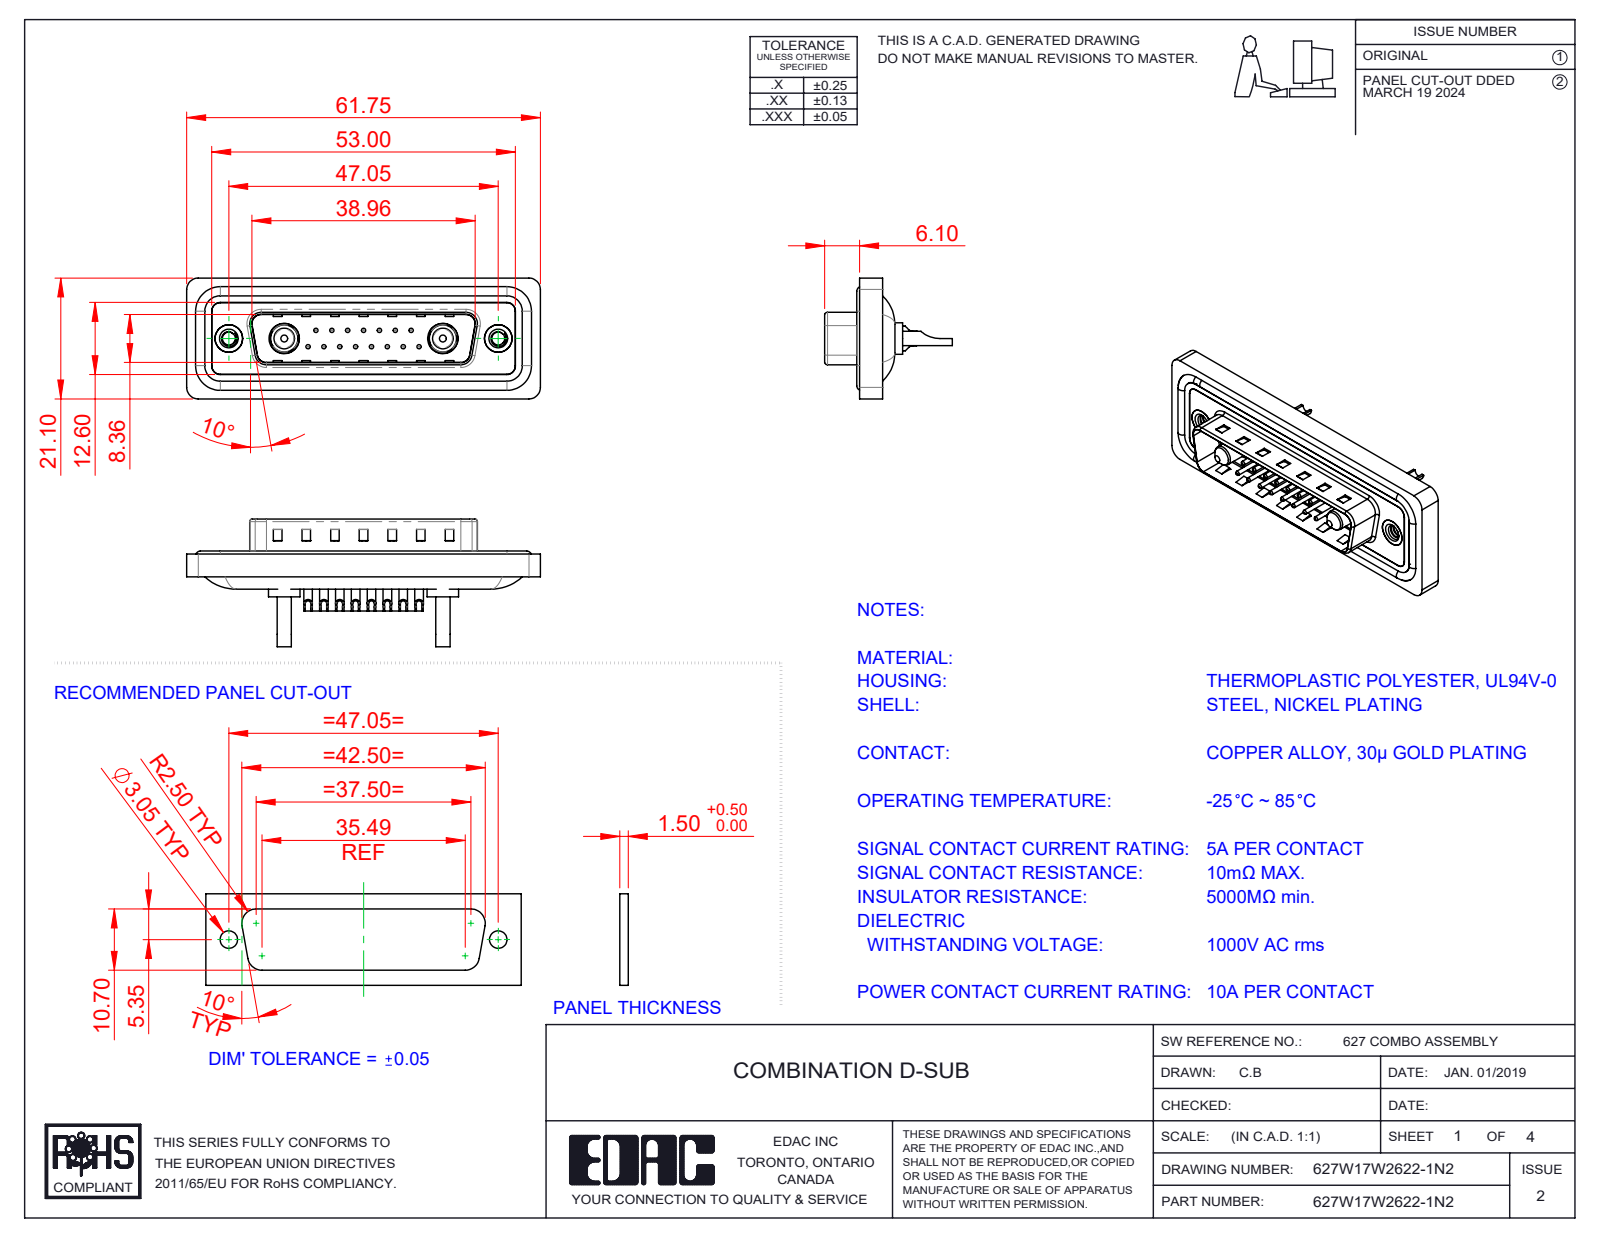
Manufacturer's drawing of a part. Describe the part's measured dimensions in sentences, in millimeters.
The part is named "627Combo Contact Row 1_22; 627Combo Threaded Rivet_2; 627Combo Housing_17W2; 627Combo Contact Row 2_22 (+5 more)". Its 3-D file was written by "SolidWorks 2023 (CONFIG_CONTROL_DESIGN)". It is 26 solids with 1128 faces: 368 planar, 472 cylindrical and 288 other. Overall it measures 61.75 by 22.3 by 21.1 millimeters. Its volume is 7 284 cubic millimeters and its surface area 12 129 square millimeters. Round holes: 15 of diameter 0.75, 15 of diameter 1, 15 of diameter 1.6, 15 of diameter 2, 2 of diameter 1.7, 2 of diameter 2.26, 2 of diameter 4, 2 of diameter 4.8, 2 of diameter 4.85, 2 of diameter 5, 2 of diameter 5.3. Round bosses or shafts: 15 of diameter 1.5, 4 of diameter 1.6, 2 of diameter 5.5, 2 of diameter 5.2, 2 of diameter 4.9, 2 of diameter 4.75, 2 of diameter 3.75, 2 of diameter 3.6. Partial cylindrical surfaces (rounded edges, fillets, slot ends): 22 of radius 1.5, 18 of radius 2, 8 of radius 0.5, 8 of radius 1.6, 6 of radius 1, 4 of radius 0.25, 4 of radius 0.6, 4 of radius 0.65. The main face-to-face distances are 0.4, 1.5, 1.1, 1.6, 0.5, 3.1, 2.9, 0.82, 9.58, 4.1. The hole center spacings are 3.16, 2.77, 5.54, 8.31, 5.04, 7.49, 11.08, 5.03.
